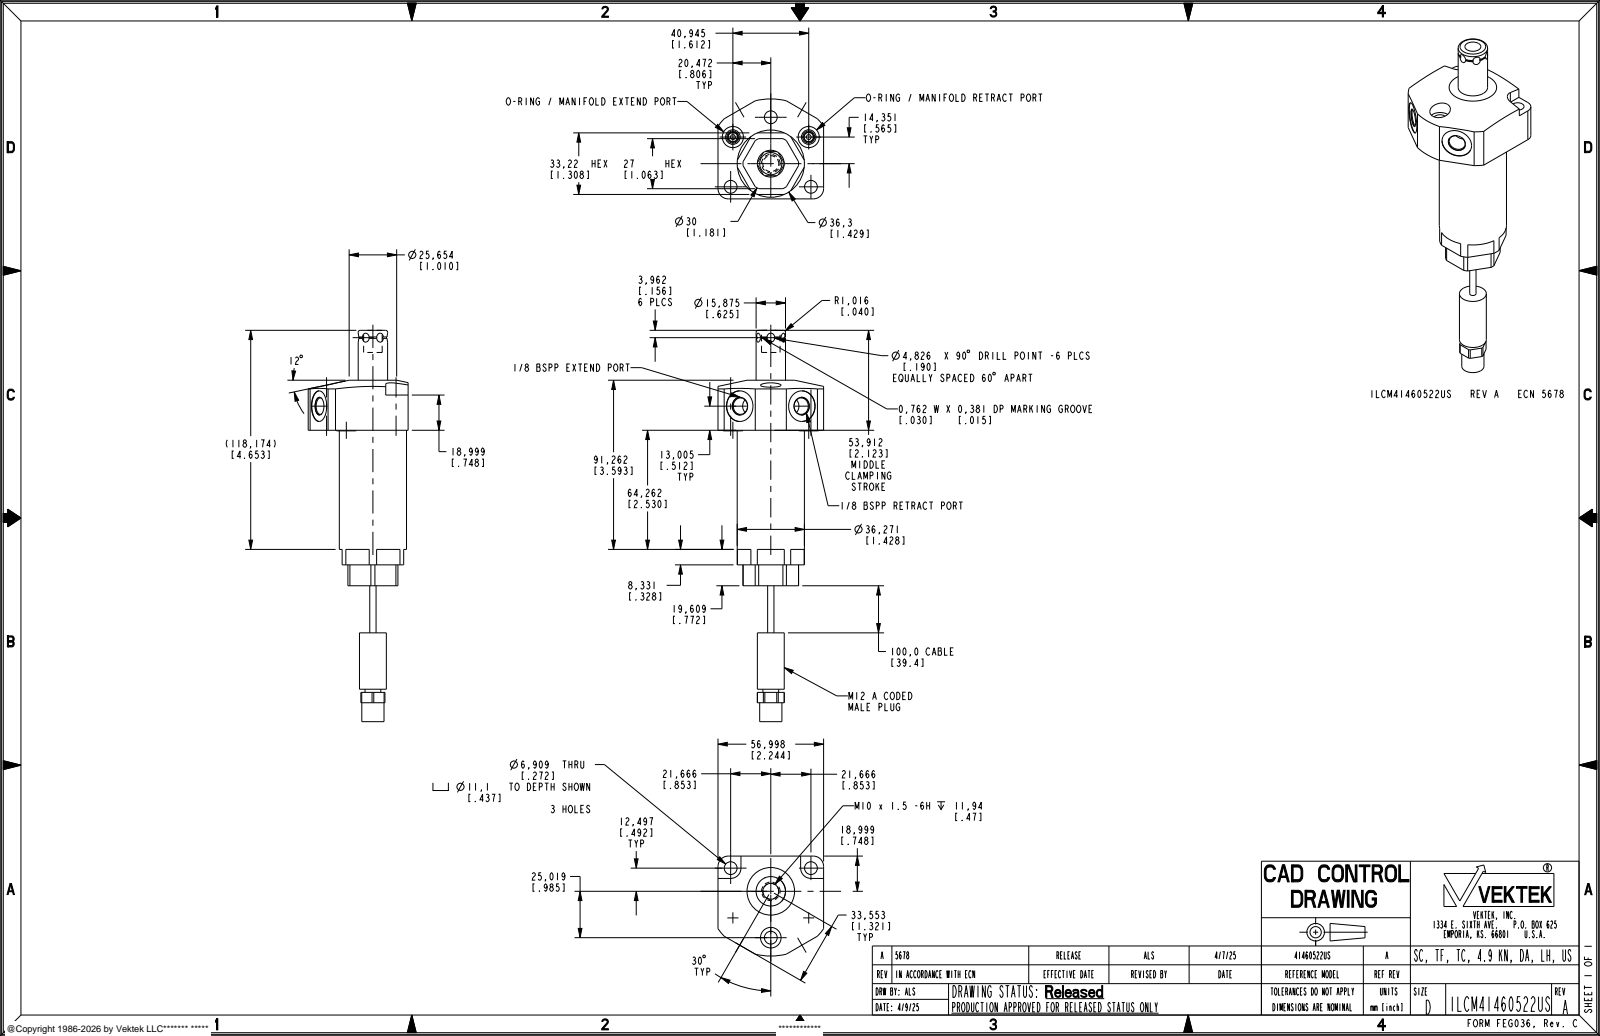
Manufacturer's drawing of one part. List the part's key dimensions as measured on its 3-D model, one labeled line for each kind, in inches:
Part name (STEP PRODUCT): ILCM41460522US
STEP written by: CREO PARAMETRIC BY PTC INC, 2021164 (AUTOMOTIVE_DESIGN)
Units: inches
Bodies: 1 solid, 198 faces (89 planar, 75 cylindrical, 34 other)
Overall size (bounding box): 8.311 × 2.444 × 2.373
Volume: 9.581 in³ · Surface area: 42.06 in²
Round holes (diameter × count): ⌀0.272 ×3, ⌀0.098 ×2, ⌀0.256 ×2, ⌀0.348 ×2, ⌀0.449 ×2, ⌀0.65 ×2, ⌀0.339 ×1, ⌀0.437 ×1
Round bosses / shafts (diameter × count): ⌀0.216 ×2, ⌀1.428 ×1, ⌀0.625 ×1, ⌀0.571 ×1, ⌀0.472 ×1, ⌀0.394 ×1, ⌀0.335 ×1, ⌀0.134 ×1
Partial cylindrical surfaces — rounded edges, fillets, slot ends (radius × count): R0.219 ×2, R0.219 ×2, R0.298 ×1, R0.591 ×1, R1.375 ×1
Main face-to-face distances: 1.063, 2.244, 0.122, 1.185, 3.302, 1.308, 4.365, 0.444, 2.858, 3.921
Hole centre spacings: 0.985, 0.909, 0.984, 1.058, 1.706, 1.967, 1.612, 1.706
